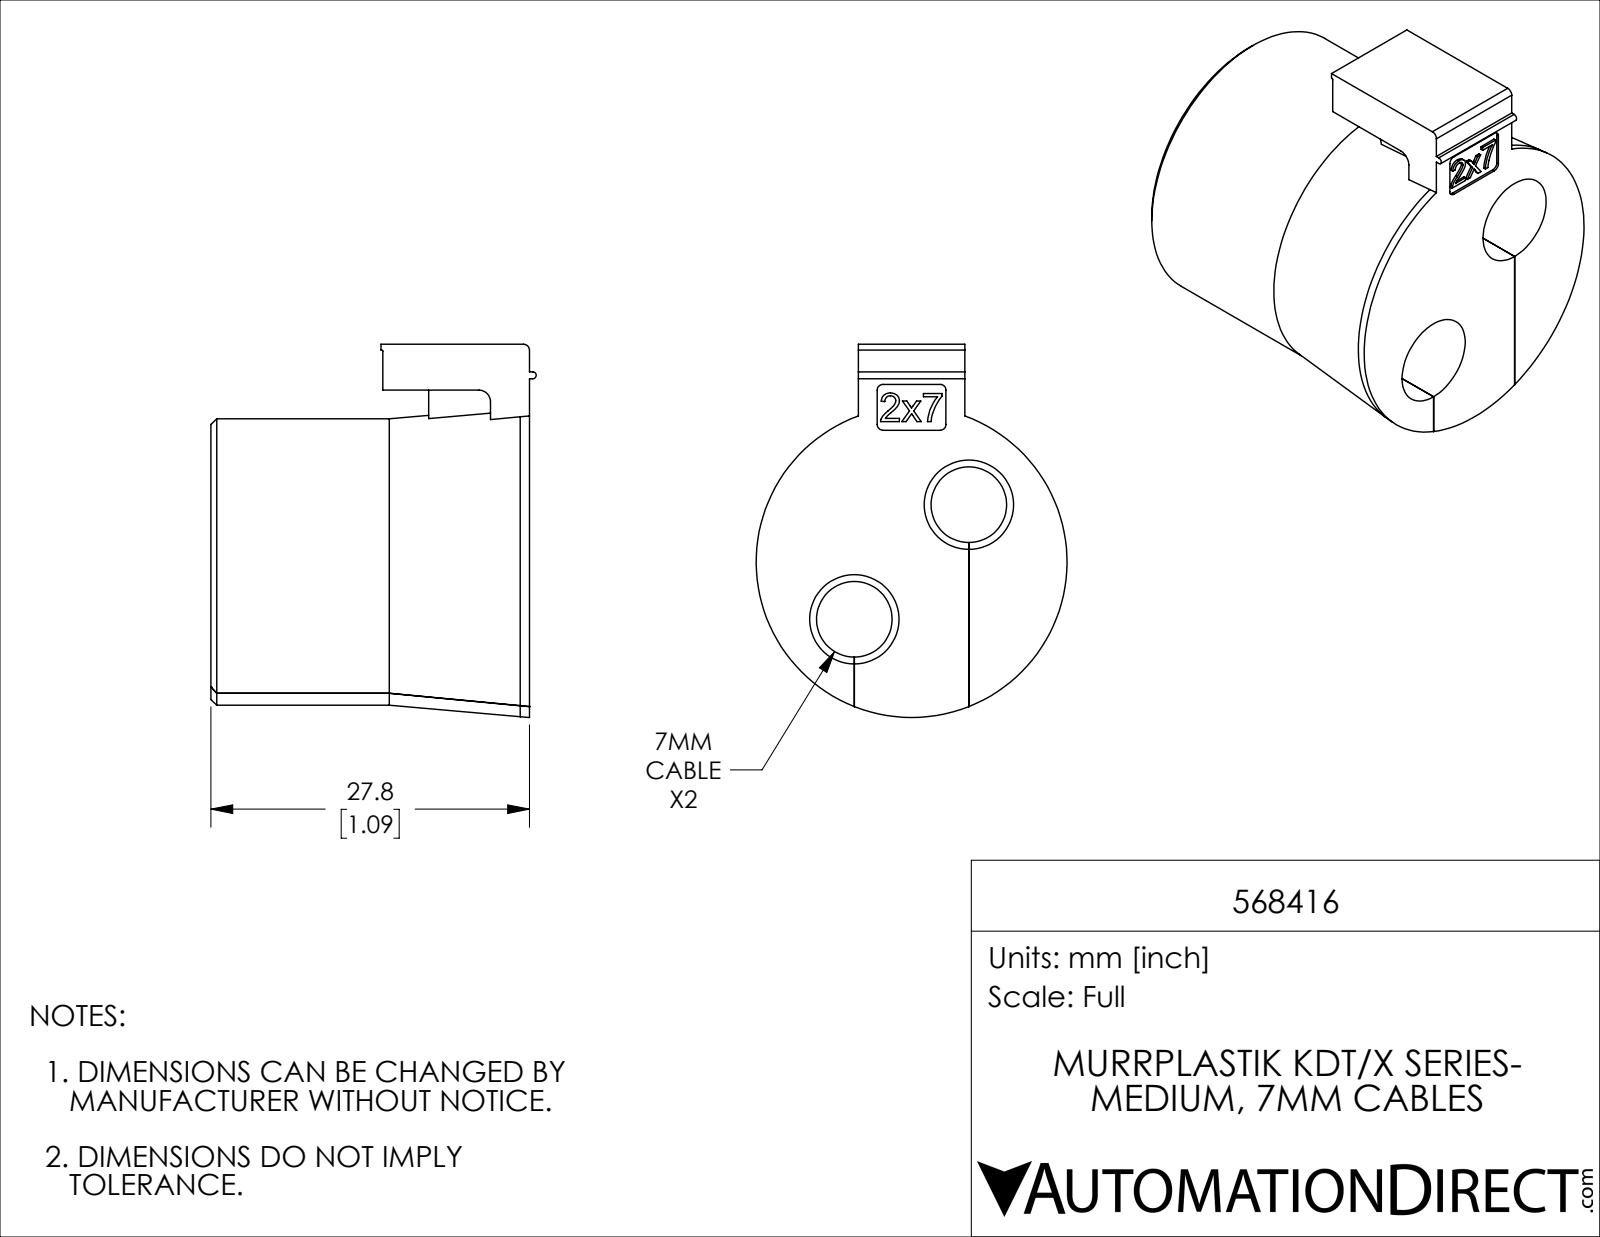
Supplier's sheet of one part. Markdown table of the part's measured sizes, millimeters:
| quantity | value |
| --- | --- |
| part name | 568416 |
| STEP written by | SolidWorks 2019 (CONFIG_CONTROL_DESIGN) |
| units | millimeters |
| bodies | 1 solid, 121 faces (51 planar, 32 cylindrical, 38 other) |
| overall size | 32.6 × 28.4 × 27.2 |
| volume | 12 100 mm³ |
| surface area | 5 725 mm² |
| round holes (diameter × count) | 6.6 × 2, 7.8 × 2 |
| round bosses / shafts (diameter × count) | 25 × 1 |
| partial cylindrical surfaces (radius × count) | 0.5 × 5, 0.1 × 1, 0.3 × 1, 1 × 1 |
| main face-to-face distances | 27.8, 0.3, 9.7, 10, 10, 10, 10, 4, 0.4, 9.7 |
| hole center spacings | 14.1 |
